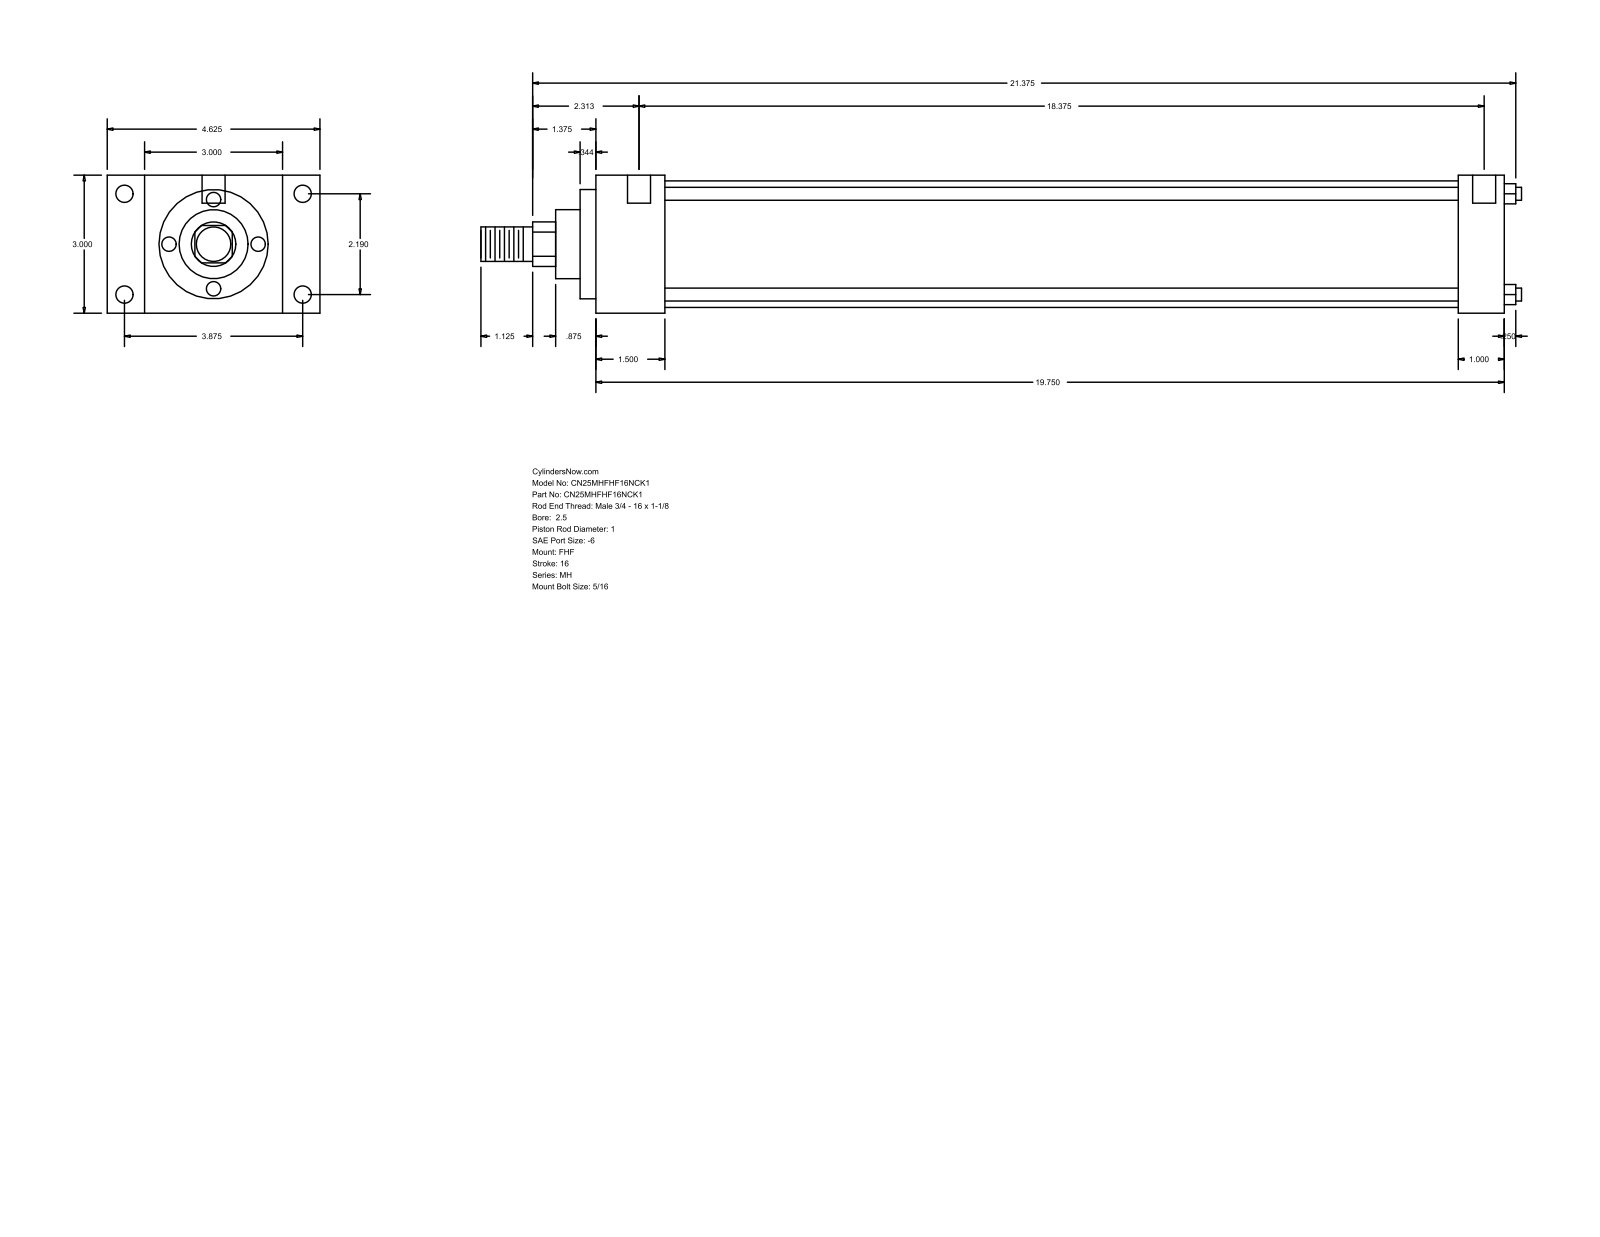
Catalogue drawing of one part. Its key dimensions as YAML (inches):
part_name: "MH_FHF__0250_1"
step_written_by: "GSSL Pune (CONFIG_CONTROL_DESIGN)"
units: inches
bodies: {solids: 0, faces: 90, planar: 61, cylindrical: 29, other: 0}
overall_size: [22.625, 4.625, 3]
round_holes:
  - {diameter: 0.219, count: 4}
  - {diameter: 0.375, count: 4}
  - {diameter: 0.5, count: 2}
round_bosses_or_shafts:
  - {diameter: 0.281, count: 4}
  - {diameter: 2.75, count: 1}
  - {diameter: 2.375, count: 1}
  - {diameter: 1.5, count: 1}
  - {diameter: 1, count: 1}
  - {diameter: 0.75, count: 1}
partial_cylinders:
  - {radius: 0.484, count: 1}
face_to_face_distances: [3, 19.75, 1.5, 18.25, 0.813, 3.813, 4.625, 18.75, 17.25, 1]
hole_center_spacings: [2.19, 3.875, 4.451, 18.687, 0.125, 0.187, 18.375, 18.5]
